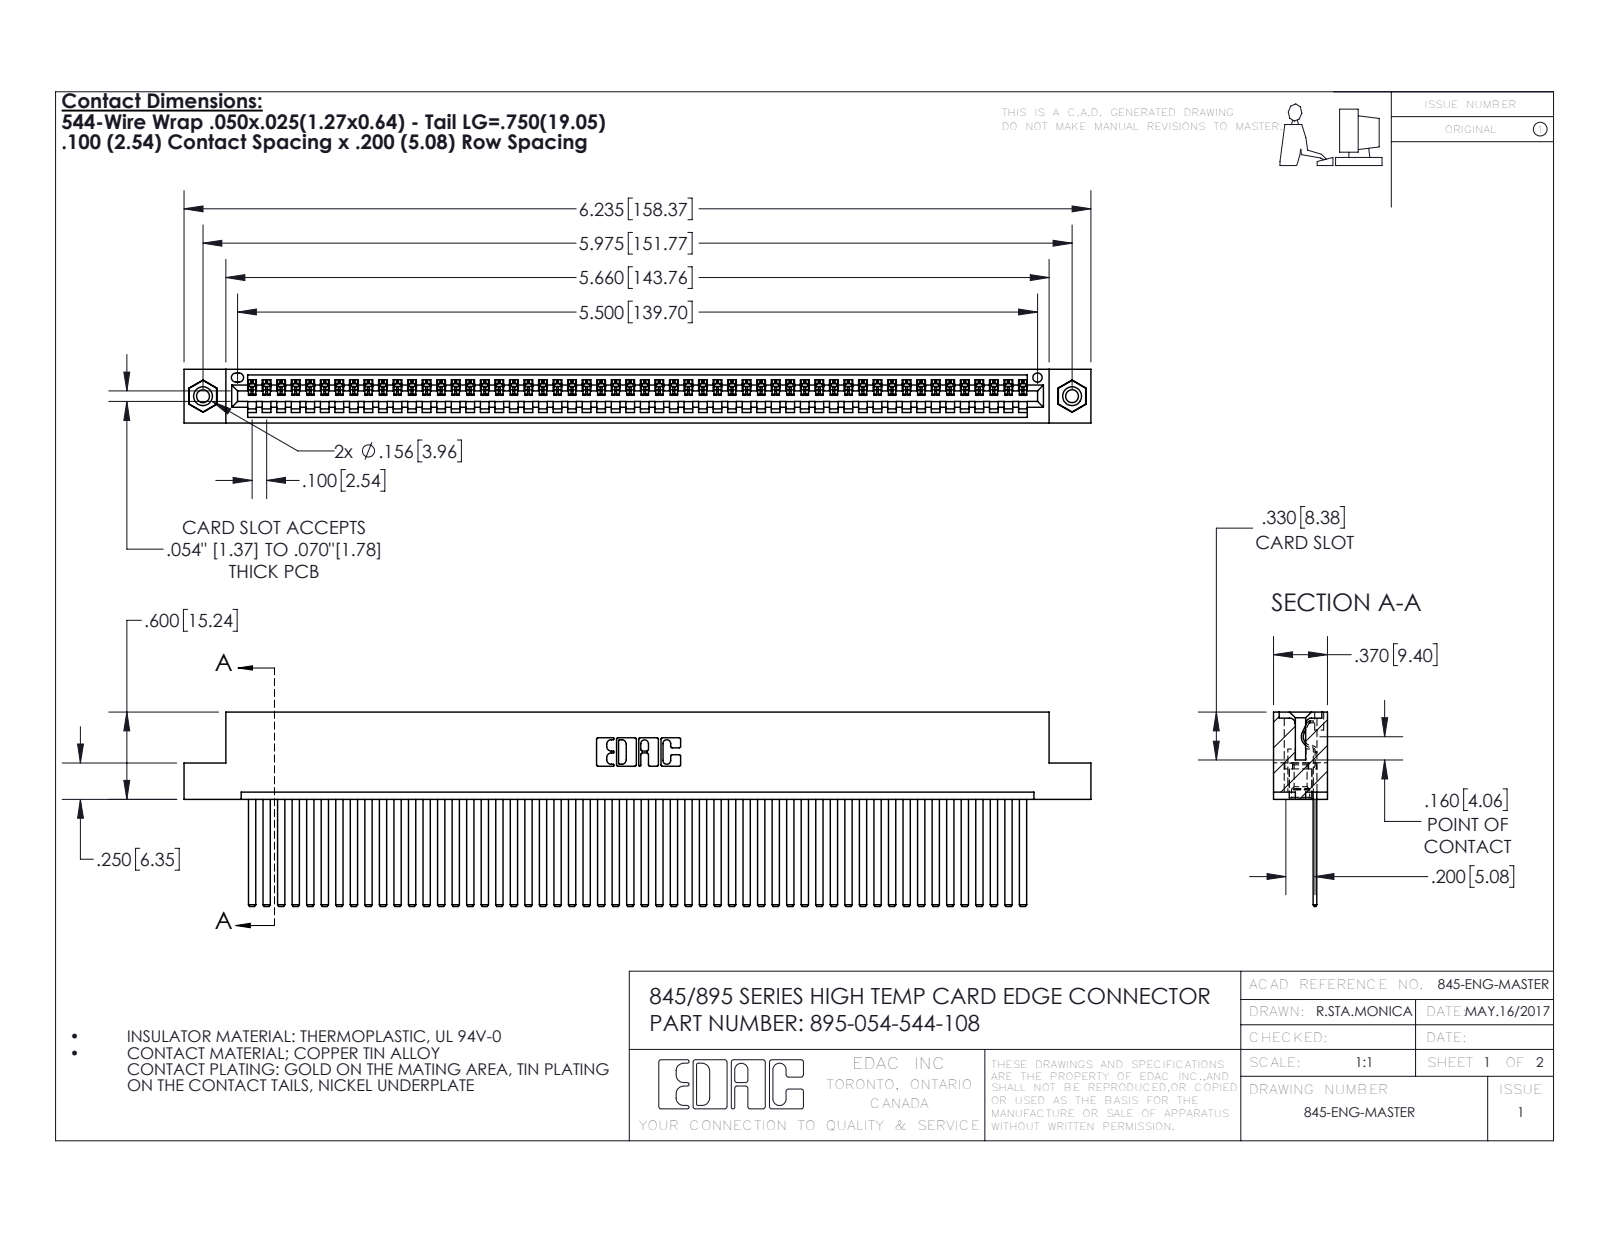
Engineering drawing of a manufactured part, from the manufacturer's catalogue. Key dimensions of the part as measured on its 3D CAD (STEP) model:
Part name (STEP PRODUCT): 345 Part_Flush Mounting Lugs - 0.156 Dia-TI; 395-054-544-108; 345-250-001_345-250-003-102; 345-292-001_345-293-144
STEP written by: SolidWorks 2016 (CONFIG_CONTROL_DESIGN)
Units: inches
Bodies: 57 solids, 2994 faces (2056 planar, 922 cylindrical, 16 other)
Overall size (bounding box): 6.235 × 1.337 × 0.37
Volume: 0.962 in³ · Surface area: 35.65 in²
Round holes (diameter × count): ⌀0.089 ×2, ⌀0.125 ×2, ⌀0.156 ×2, ⌀0.064 ×1
Round bosses / shafts (diameter × count): ⌀0.155 ×2
Partial cylindrical surfaces — rounded edges, fillets, slot ends (radius × count): R0.006 ×108, R0.01 ×22, R0.007 ×6, R0.031 ×6, R0.026 ×3, R0.031 ×2, R0.04 ×2, R0.014 ×1
Main face-to-face distances: 0.072, 0.298, 0.025, 0.098, 0.272, 0.37, 0.2, 0.225, 0.149, 0.072
Hole centre spacings: 0.27, 5.739, 5.975
